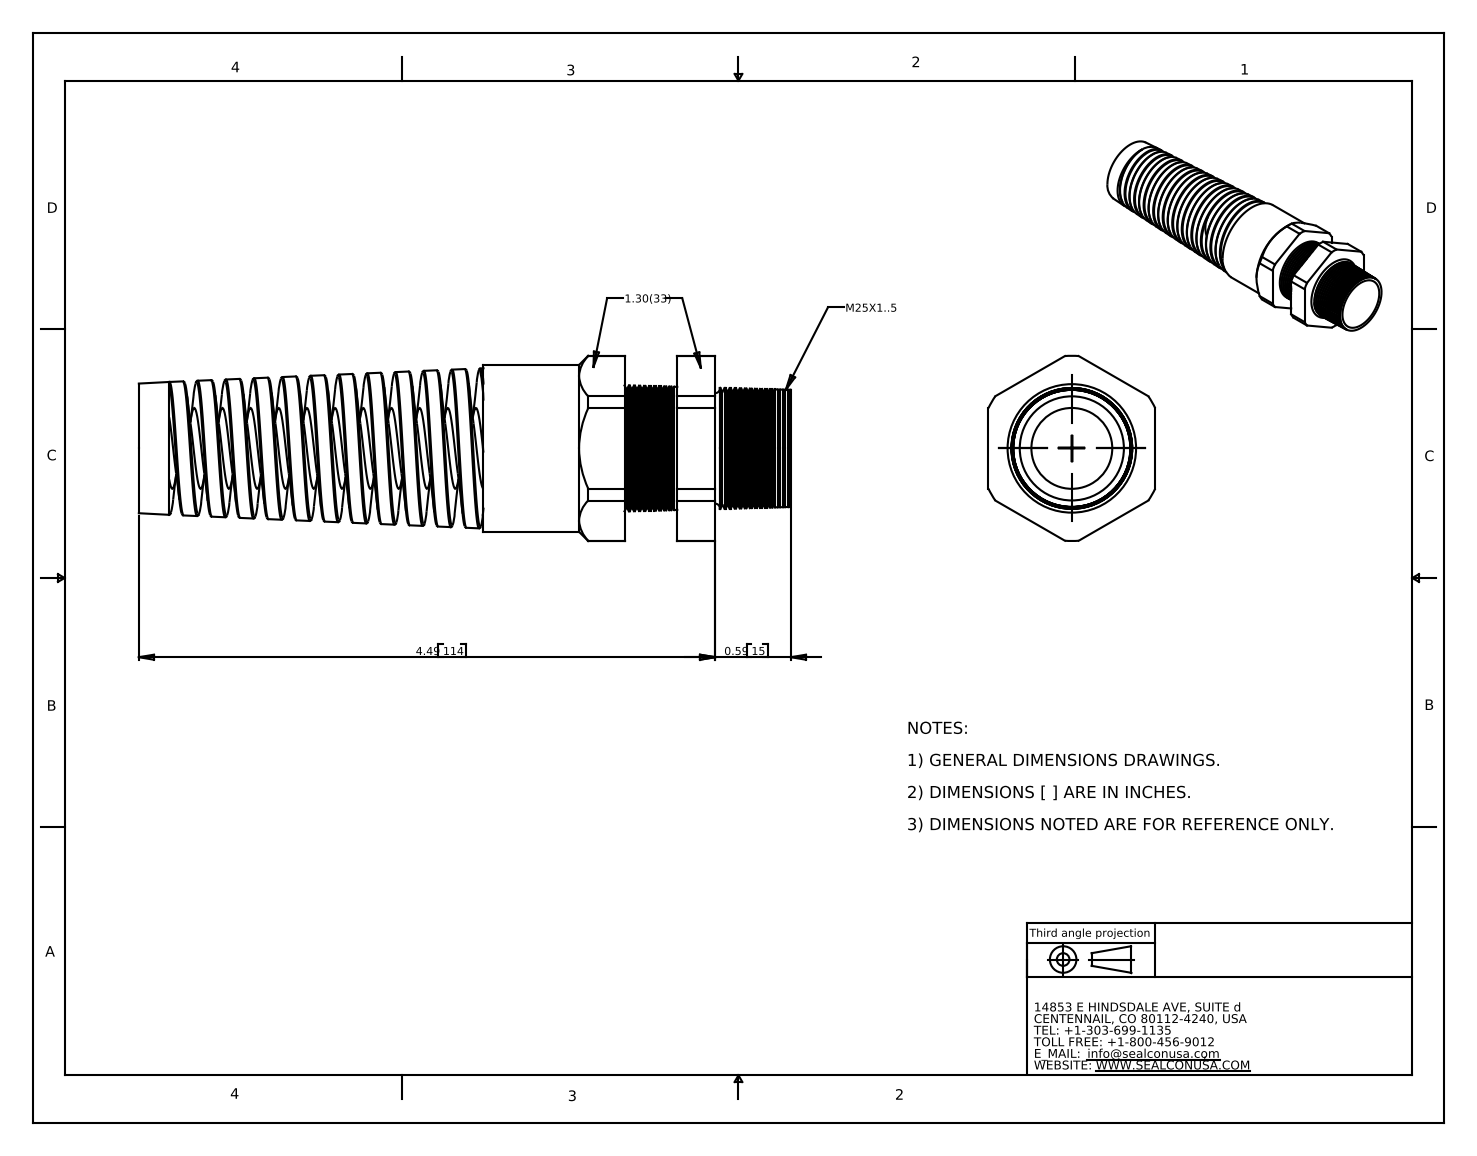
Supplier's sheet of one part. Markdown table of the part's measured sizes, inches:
| quantity | value |
| --- | --- |
| part name | CF25DR-GY |
| STEP written by | SolidWorks 2007 (CONFIG_CONTROL_DESIGN) |
| units | inches |
| bodies | 2 solids, 264 faces (25 planar, 47 cylindrical, 192 other) |
| overall size | 5.08 × 1.443 × 1.3 |
| volume | 2.988 in³ |
| surface area | 46.49 in² |
| round holes (diameter × count) | 0.63 × 1, 0.655 × 1 |
| round bosses / shafts (diameter × count) | 1.3 × 1, 0.949 × 1 |
| partial cylindrical surfaces (radius × count) | 0.721 × 1 |
| main face-to-face distances | 1.3, 0.411, 0.706, 0.295, 3.784, 4.195, 4.491, 2.685, 1.099, 1.51 |
